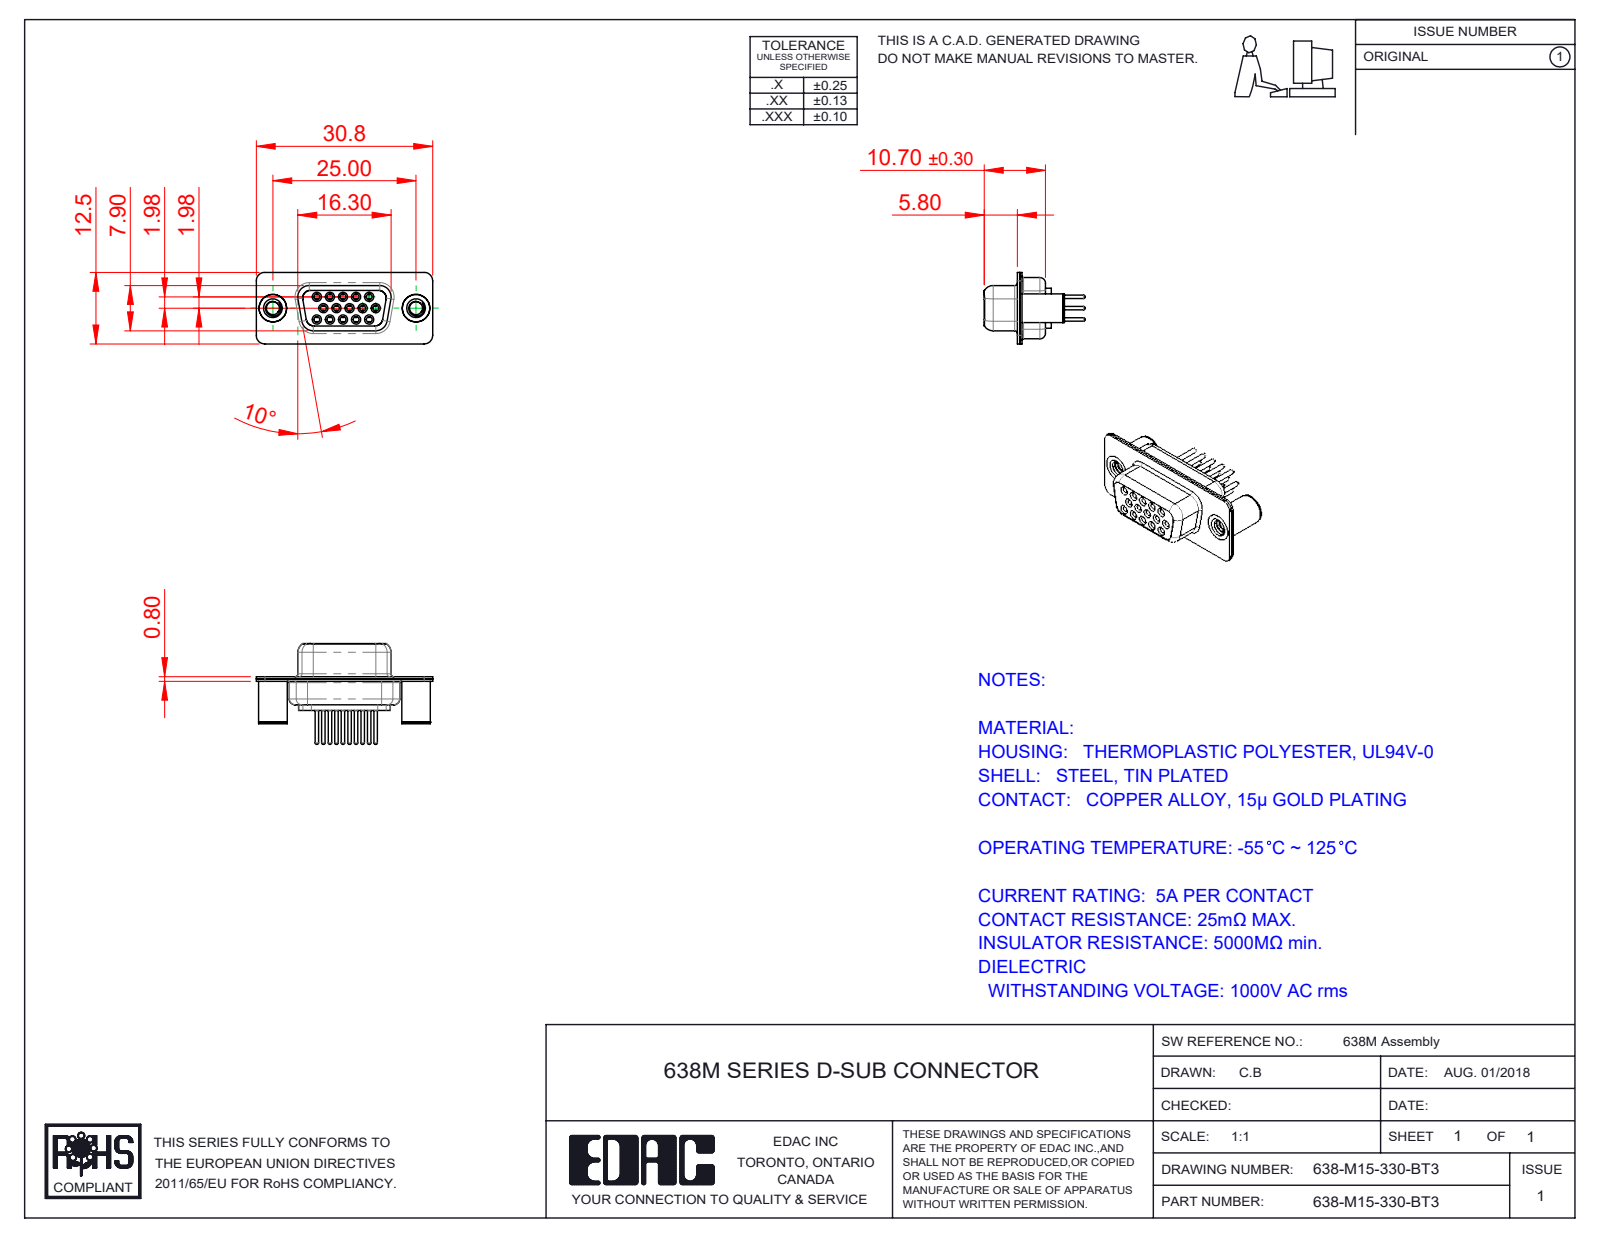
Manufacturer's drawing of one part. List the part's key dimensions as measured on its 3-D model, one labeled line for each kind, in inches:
Part name (STEP PRODUCT): 638M Contact Row 1_30; 638M Housing_15 Contacts; 638M Contact Row 2_30; 638-M15-330-BT3 (+4 more)
STEP written by: SolidWorks 2020 (CONFIG_CONTROL_DESIGN)
Units: inches
Bodies: 20 solids, 1138 faces (292 planar, 446 cylindrical, 400 other)
Overall size (bounding box): 1.213 × 0.693 × 0.492
Volume: 0.107 in³ · Surface area: 8.658 in²
Round holes (diameter × count): ⌀0.039 ×15, ⌀0.043 ×15, ⌀0.067 ×15, ⌀0.071 ×15, ⌀0.079 ×15, ⌀0.089 ×2, ⌀0.128 ×2, ⌀0.157 ×2, ⌀0.189 ×2
Round bosses / shafts (diameter × count): ⌀0.087 ×15, ⌀0.063 ×15, ⌀0.059 ×15, ⌀0.024 ×15, ⌀0.197 ×2, ⌀0.193 ×2
Partial cylindrical surfaces — rounded edges, fillets, slot ends (radius × count): R0.059 ×16, R0.079 ×12, R0.053 ×8, R0.063 ×8, R0.01 ×4, R0.02 ×4, R0.024 ×4, R0.026 ×4
Main face-to-face distances: 0.016, 0.055, 0.018, 0.333, 0.031, 0.35, 0.039, 0.071, 0.244, 0.278
Hole centre spacings: 0.09, 0.156, 0.09, 0.18, 0.238, 0.238, 0.27, 0.312
